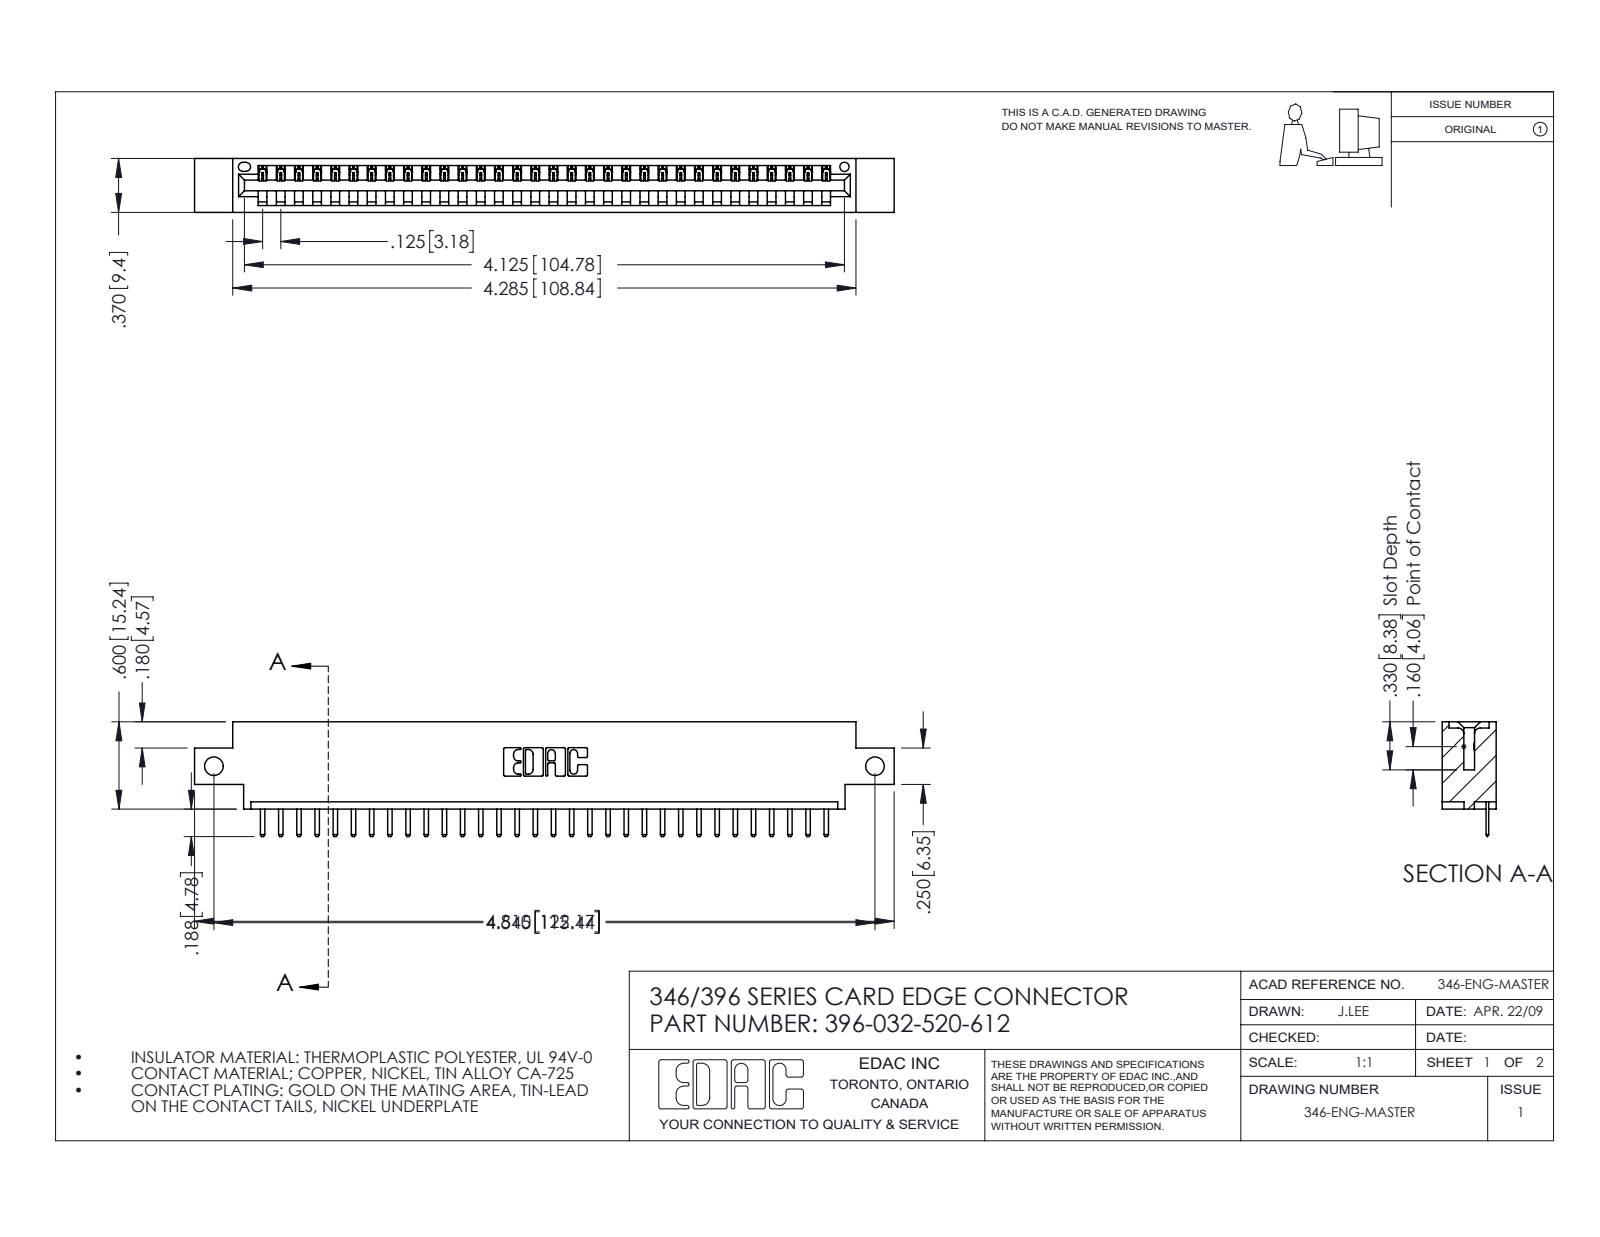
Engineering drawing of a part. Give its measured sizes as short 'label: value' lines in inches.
name: 396-032-520-612; 345-292-001_345-293-120; 346 Part_0.170 Offset - Side Mount
written by: SolidWorks 2016 (CONFIG_CONTROL_DESIGN)
unit: in
bodies: 33 solids, 2110 faces (1424 planar, 686 cylindrical, 0 other)
size: 4.81 × 0.788 × 0.37
volume: 0.689 in³; area: 21.25 in²
holes: 2× ⌀0.128, 1× ⌀0.064
rounds: 66× R0.01, 64× R0.006, 22× R0.01, 6× R0.007, 6× R0.031, 3× R0.026, 2× R0.031, 2× R0.04
face distances: 0.048, 0.322, 0.37, 0.25, 0.148, 0.222, 0.1, 0.174, 0.072, 0.298
hole spacings: 4.545
